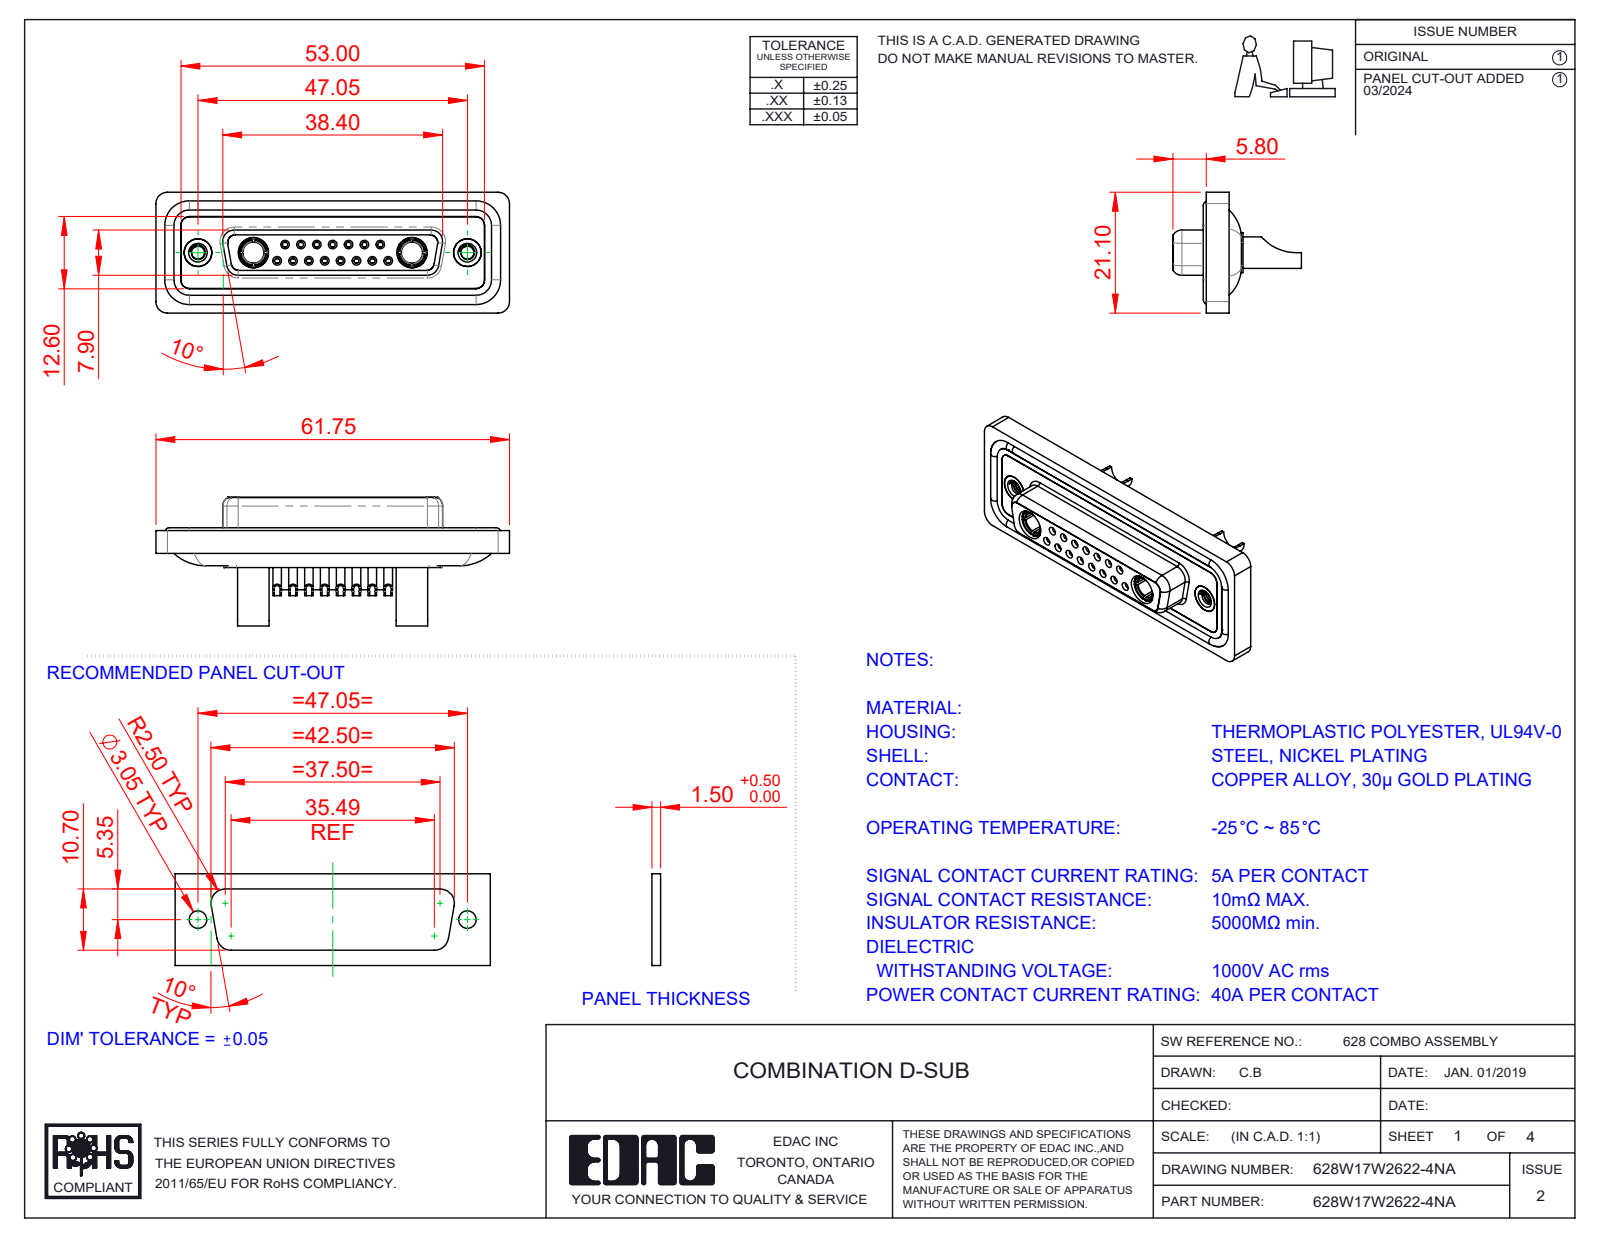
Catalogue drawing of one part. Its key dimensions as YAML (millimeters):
part_name: "628Combo Shell Front_25 Contacts; 628W17W2622-4NA; 628Combo Contact Row 2_22; 628Combo Housing_17W2 (+5 more)"
step_written_by: "SolidWorks 2023 (CONFIG_CONTROL_DESIGN)"
units: millimeters
bodies: {solids: 26, faces: 1363, planar: 422, cylindrical: 553, other: 388}
overall_size: [61.75, 22.45, 21.1]
volume: 8437
surface_area: 14292
round_holes:
  - {diameter: 0.9, count: 15}
  - {diameter: 1, count: 15}
  - {diameter: 1.1, count: 15}
  - {diameter: 1.5, count: 15}
  - {diameter: 2, count: 15}
  - {diameter: 1.6, count: 8}
  - {diameter: 1.7, count: 7}
  - {diameter: 4.85, count: 4}
  - {diameter: 2.26, count: 2}
  - {diameter: 3.7, count: 2}
  - {diameter: 4, count: 2}
  - {diameter: 4.05, count: 2}
round_bosses_or_shafts:
  - {diameter: 2.2, count: 15}
  - {diameter: 1.6, count: 11}
  - {diameter: 5.5, count: 2}
  - {diameter: 5.2, count: 2}
  - {diameter: 4.96, count: 2}
  - {diameter: 4.95, count: 2}
  - {diameter: 4.8, count: 2}
  - {diameter: 4.75, count: 2}
partial_cylinders:
  - {radius: 1.5, count: 22}
  - {radius: 2, count: 18}
  - {radius: 1.35, count: 8}
  - {radius: 1.6, count: 8}
  - {radius: 1, count: 6}
  - {radius: 0.25, count: 4}
  - {radius: 0.5, count: 4}
  - {radius: 0.6, count: 4}
face_to_face_distances: [0.4, 7.45, 1.8, 5.65, 6.6, 0.5, 7.05, 1.6, 2.9, 1.1]
hole_center_spacings: [3.16, 2.77, 8.31, 5.54, 5.03, 5.04, 7.49, 11.08]
